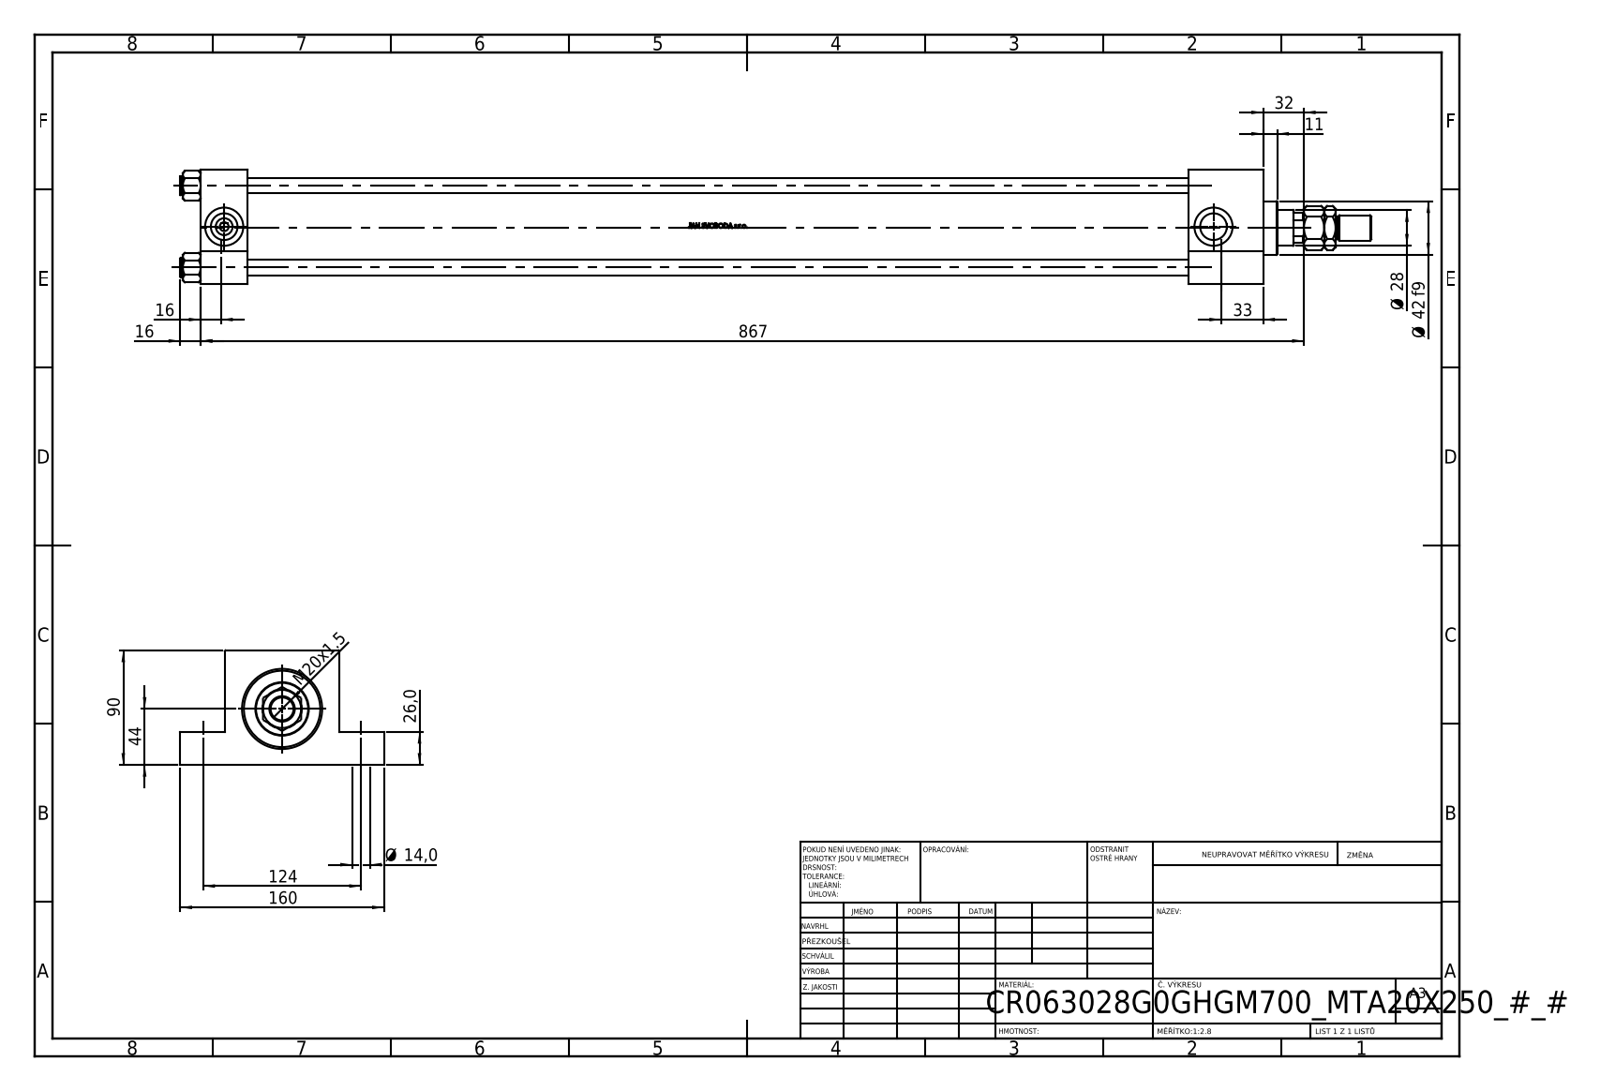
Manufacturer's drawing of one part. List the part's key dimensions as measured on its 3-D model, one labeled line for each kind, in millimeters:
Part name (STEP PRODUCT): V215_VC_A; V215CR_G_TYCINKA; NUT_M5_G; V215CR_G_Body (+2 more)
STEP written by: SolidWorks 2019 (CONFIG_CONTROL_DESIGN)
Units: millimetres
Bodies: 12 solids, 1136 faces (446 planar, 128 cylindrical, 562 other)
Overall size (bounding box): 936 × 160 × 90
Volume: 2 294 000 mm³ · Surface area: 649 626 mm²
Round holes (diameter × count): ⌀12 ×4, ⌀14 ×4, ⌀7 ×2, ⌀20.96 ×2, ⌀30 ×2, ⌀18.5 ×1, ⌀28 ×1, ⌀31 ×1, ⌀50 ×1, ⌀60 ×1, ⌀63 ×1
Round bosses / shafts (diameter × count): ⌀15 ×4, ⌀69 ×1, ⌀42 ×1, ⌀20 ×1, ⌀18 ×1
Partial cylindrical surfaces — rounded edges, fillets, slot ends (radius × count): R13.5 ×1
Main face-to-face distances: 90, 37, 835, 798, 776, 739, 59, 26, 64, 35
Hole centre spacings: 64.3, 44.77, 46.18, 90.93, 124, 786, 795.72, 777.5
